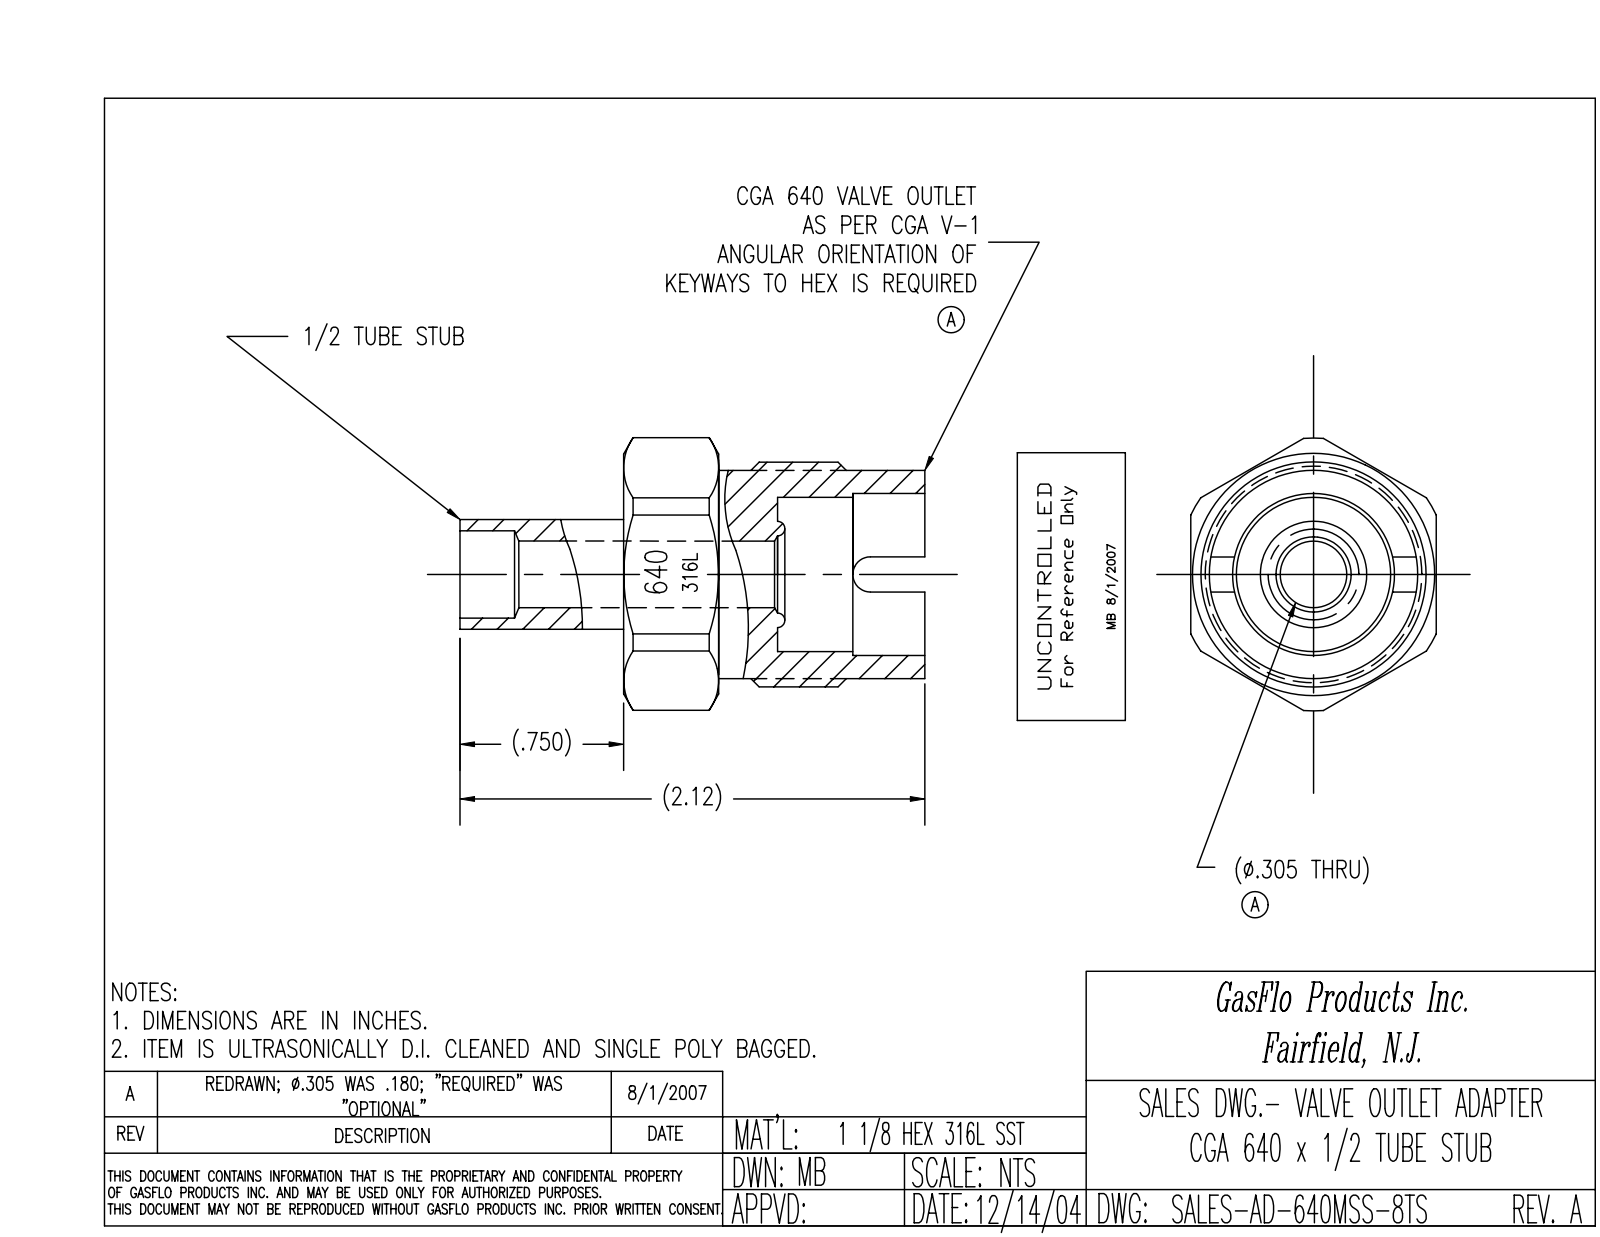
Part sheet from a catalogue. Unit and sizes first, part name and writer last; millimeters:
Units: millimetres
Overall size (bounding box): 53.8 × 31.8 × 28.6
Round holes (diameter × count): ⌀7.7 ×1, ⌀8.5 ×1, ⌀10.2 ×1, ⌀18 ×1, ⌀18.8 ×1
Round bosses / shafts (diameter × count): ⌀26.1 ×1, ⌀23.4 ×1, ⌀23.4 ×1, ⌀12.8 ×1, ⌀12.7 ×1
Partial cylindrical surfaces — rounded edges, fillets, slot ends (radius × count): R2.1 ×1, R15.9 ×1
Main face-to-face distances: 28.6, 10.7, 24, 34.7, 17, 7, 17.7, 16.2, 0.8, 7.8
Volume: 14 300 mm³ · Surface area: 7 290 mm²
Bodies: 1 solid, 163 faces (65 planar, 38 cylindrical, 60 other)
Part name (STEP PRODUCT): AD-640MSS-8TS
STEP written by: SolidWorks 2018 (CONFIG_CONTROL_DESIGN)
